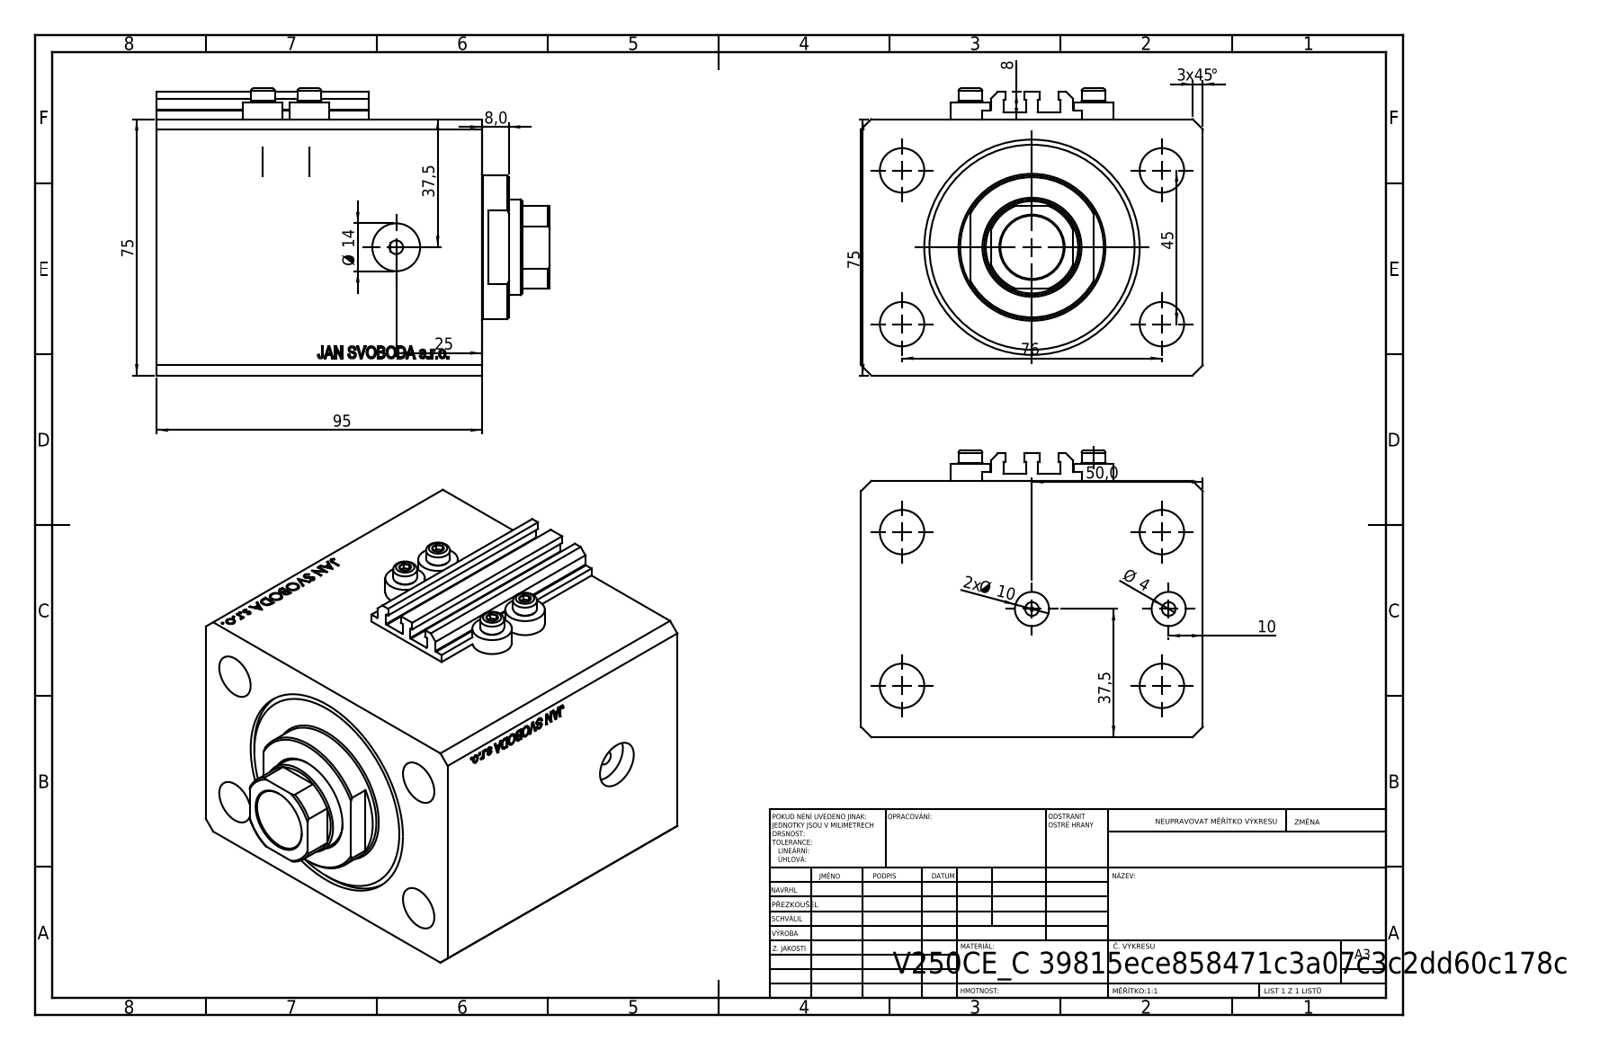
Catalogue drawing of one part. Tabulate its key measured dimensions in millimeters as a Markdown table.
| quantity | value |
| --- | --- |
| part name | V250CE_C_VCP; V250CE_C_Body; V250CE_VC_C; ALLEN BOLT V250CE |
| STEP written by | SolidWorks 2019 (CONFIG_CONTROL_DESIGN) |
| units | millimeters |
| bodies | 8 solids, 1038 faces (504 planar, 88 cylindrical, 446 other) |
| overall size | 114.9 × 100 × 84 |
| volume | 647 653 mm³ |
| surface area | 119 087 mm² |
| round holes (diameter × count) | 4 × 8, 13 × 4, 10 × 2, 14 × 2, 1.25 × 1, 18.5 × 1, 28 × 1, 50 × 1, 63 × 1 |
| round bosses / shafts (diameter × count) | 11.6 × 4, 7 × 4, 42 × 1 |
| partial cylindrical surfaces (radius × count) | 0.2 × 10, 13.5 × 1 |
| main face-to-face distances | 75, 100, 95, 11.9, 83.1, 68.4, 56.5, 26.6, 48.4, 36.5 |
| hole center spacings | 44.16, 45, 13.6, 22.59, 36, 38.48, 76, 81.18 |
